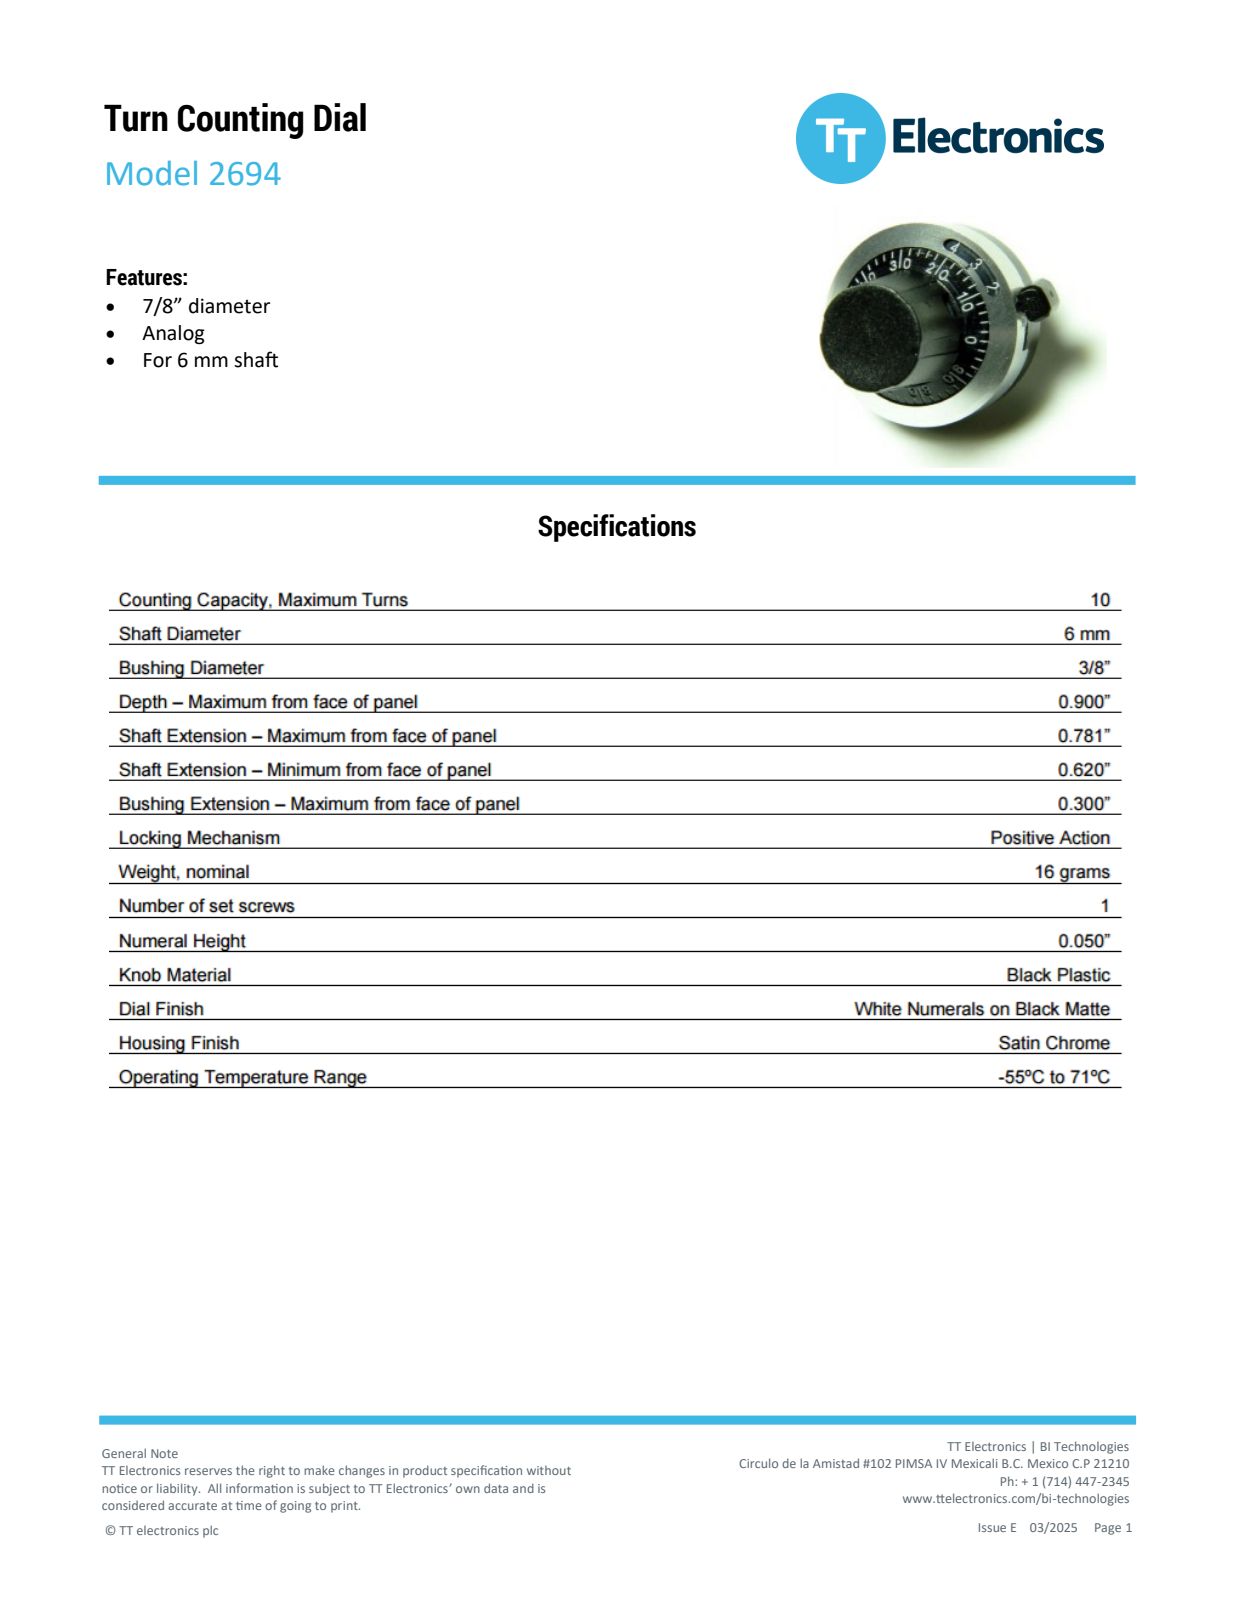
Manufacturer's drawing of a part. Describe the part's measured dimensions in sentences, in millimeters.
The part is named "2696-3; 2696-15_ASM; 2696-5; 2696-16_ASM (+8 more)". Its 3-D file was written by "CREO PARAMETRIC BY PTC INC, 2016130 (CONFIG_CONTROL_DESIGN)". It is 11 solids with 2304 faces: 1897 planar, 323 cylindrical and 84 other. Overall it measures 24.2 by 22 by 22 millimeters. Its volume is 6 058 cubic millimeters and its surface area 6 419 square millimeters. Round holes: 1 of diameter 6, 1 of diameter 6.97, 1 of diameter 8.96, 1 of diameter 9.96, 1 of diameter 12.28, 1 of diameter 14.35, 1 of diameter 17.28, 1 of diameter 17.3, 1 of diameter 19.05, 1 of diameter 21.16, 1 of diameter 21.68. Round bosses or shafts: 1 of diameter 22, 1 of diameter 22, 1 of diameter 21.8, 1 of diameter 21.67, 1 of diameter 21.12, 1 of diameter 19.04, 1 of diameter 18.72, 1 of diameter 6.7. Partial cylindrical surfaces (rounded edges, fillets, slot ends): 60 of radius 0.88, 13 of radius 0.24, 7 of radius 0.8, 6 of radius 0.16, 6 of radius 0.78, 5 of radius 0.48, 3 of radius 0.13, 2 of radius 0.17. The main face-to-face distances are 1.58, 1.36, 5.14, 4.92, 6.5, 1.42, 1.2, 6.34, 0.72, 0.64.
